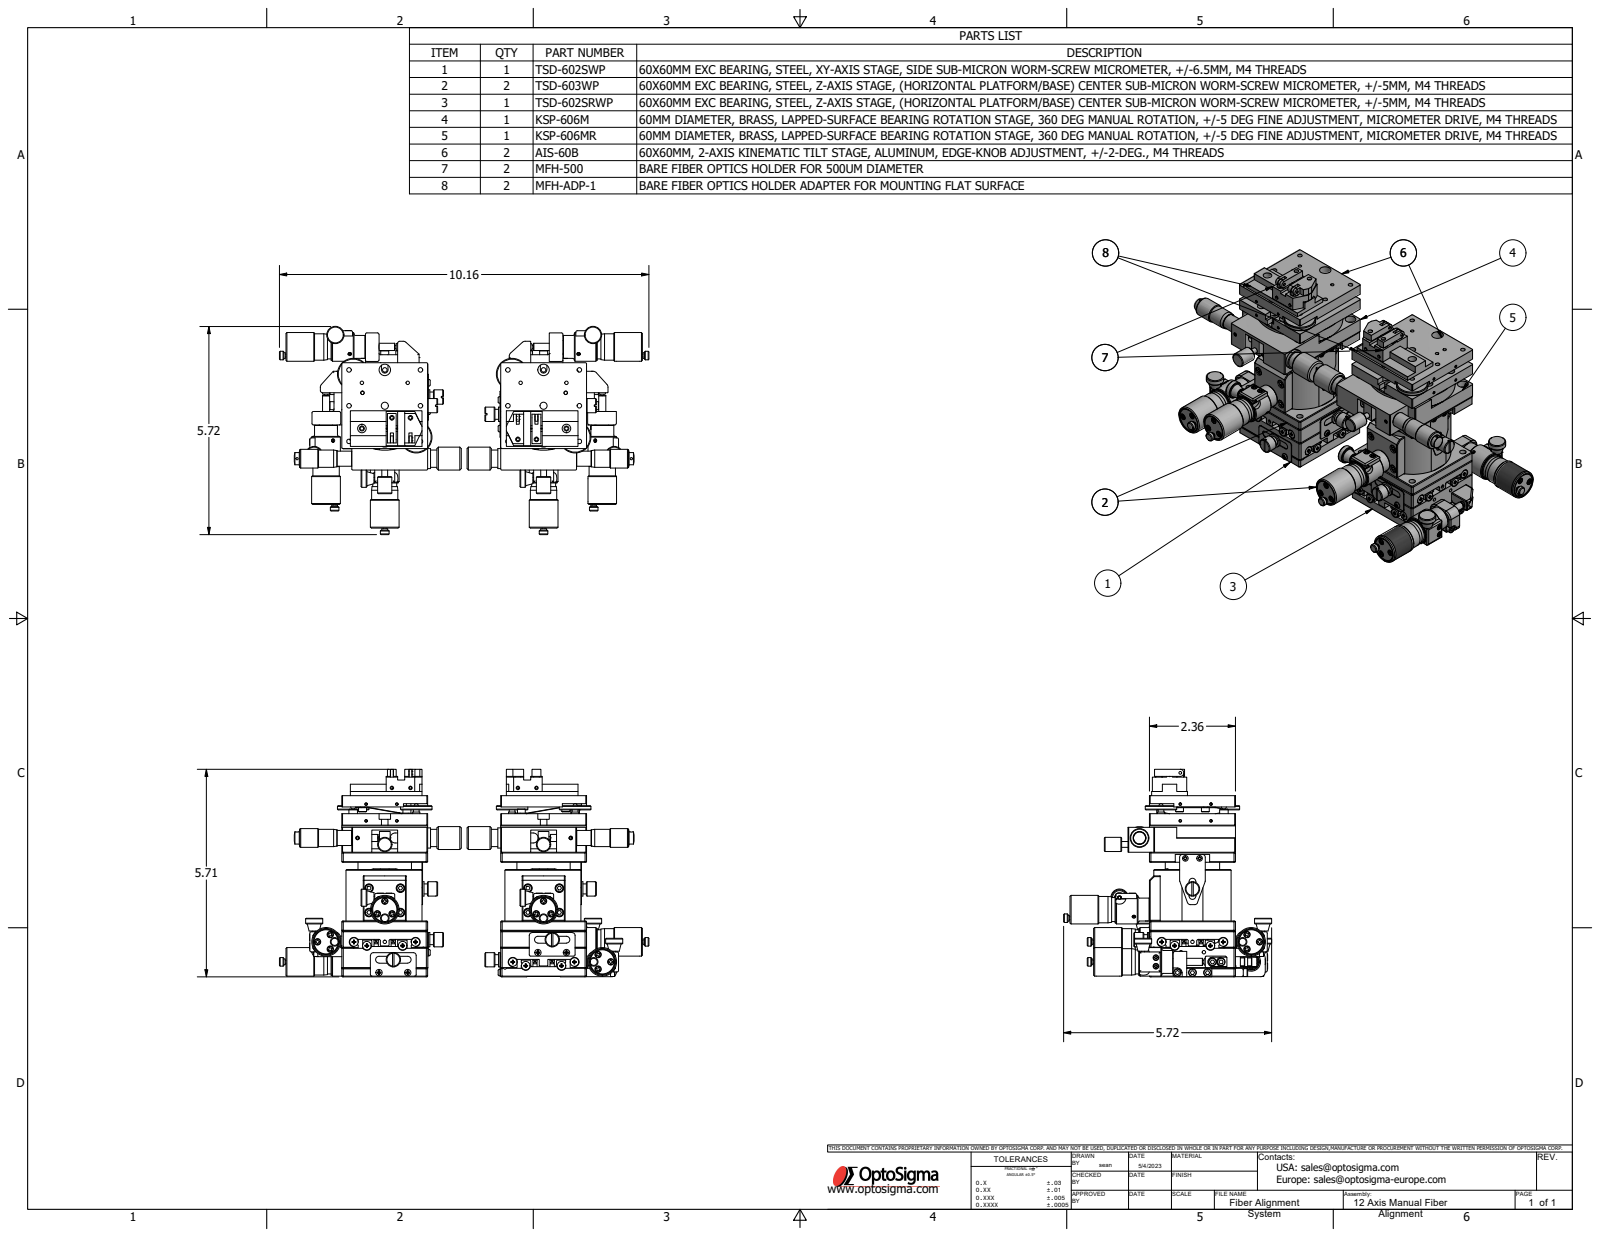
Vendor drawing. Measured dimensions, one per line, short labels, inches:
name: Multi-Axis Fiber alignment system; TSD-602SWP; TSD-602SWP-C1-S08; TSD-602SWP-C1-S10 (+8 more)
written by: Autodesk Inventor 2022 (AUTOMOTIVE_DESIGN)
unit: in
bodies: 159 solids, 7957 faces (4374 planar, 2474 cylindrical, 1109 other)
size: 10.157 × 5.72 × 5.709
volume: 46.55 in³; area: 601.6 in²
holes: 88× ⌀0.071, 78× ⌀0.097, 37× ⌀0.128, 33× ⌀0.062, 28× ⌀0.087, 28× ⌀0.118, 28× ⌀0.315, 27× ⌀0.236, 26× ⌀0.083, 22× ⌀0.177, 21× ⌀0.062, 19× ⌀0.098
bosses: 86× ⌀0.157, 63× ⌀0.079, 36× ⌀0.217, 34× ⌀0.118, 26× ⌀0.236, 24× ⌀0.138, 19× ⌀0.276, 19× ⌀0.177
rounds: 261× R0.039, 128× R0.012, 94× R0.079, 64× R0.031, 32× R0.118, 28× R0.128, 22× R0.02, 14× R0.197
face distances: 2.362, 0.748, 2.913, 2.165, 0.669, 0.807, 1.555, 0.354, 4.369, 0.551
hole spacings: 0.236, 0.413, 0.498, 1.457, 1.478, 1.953, 2.398, 0.138
